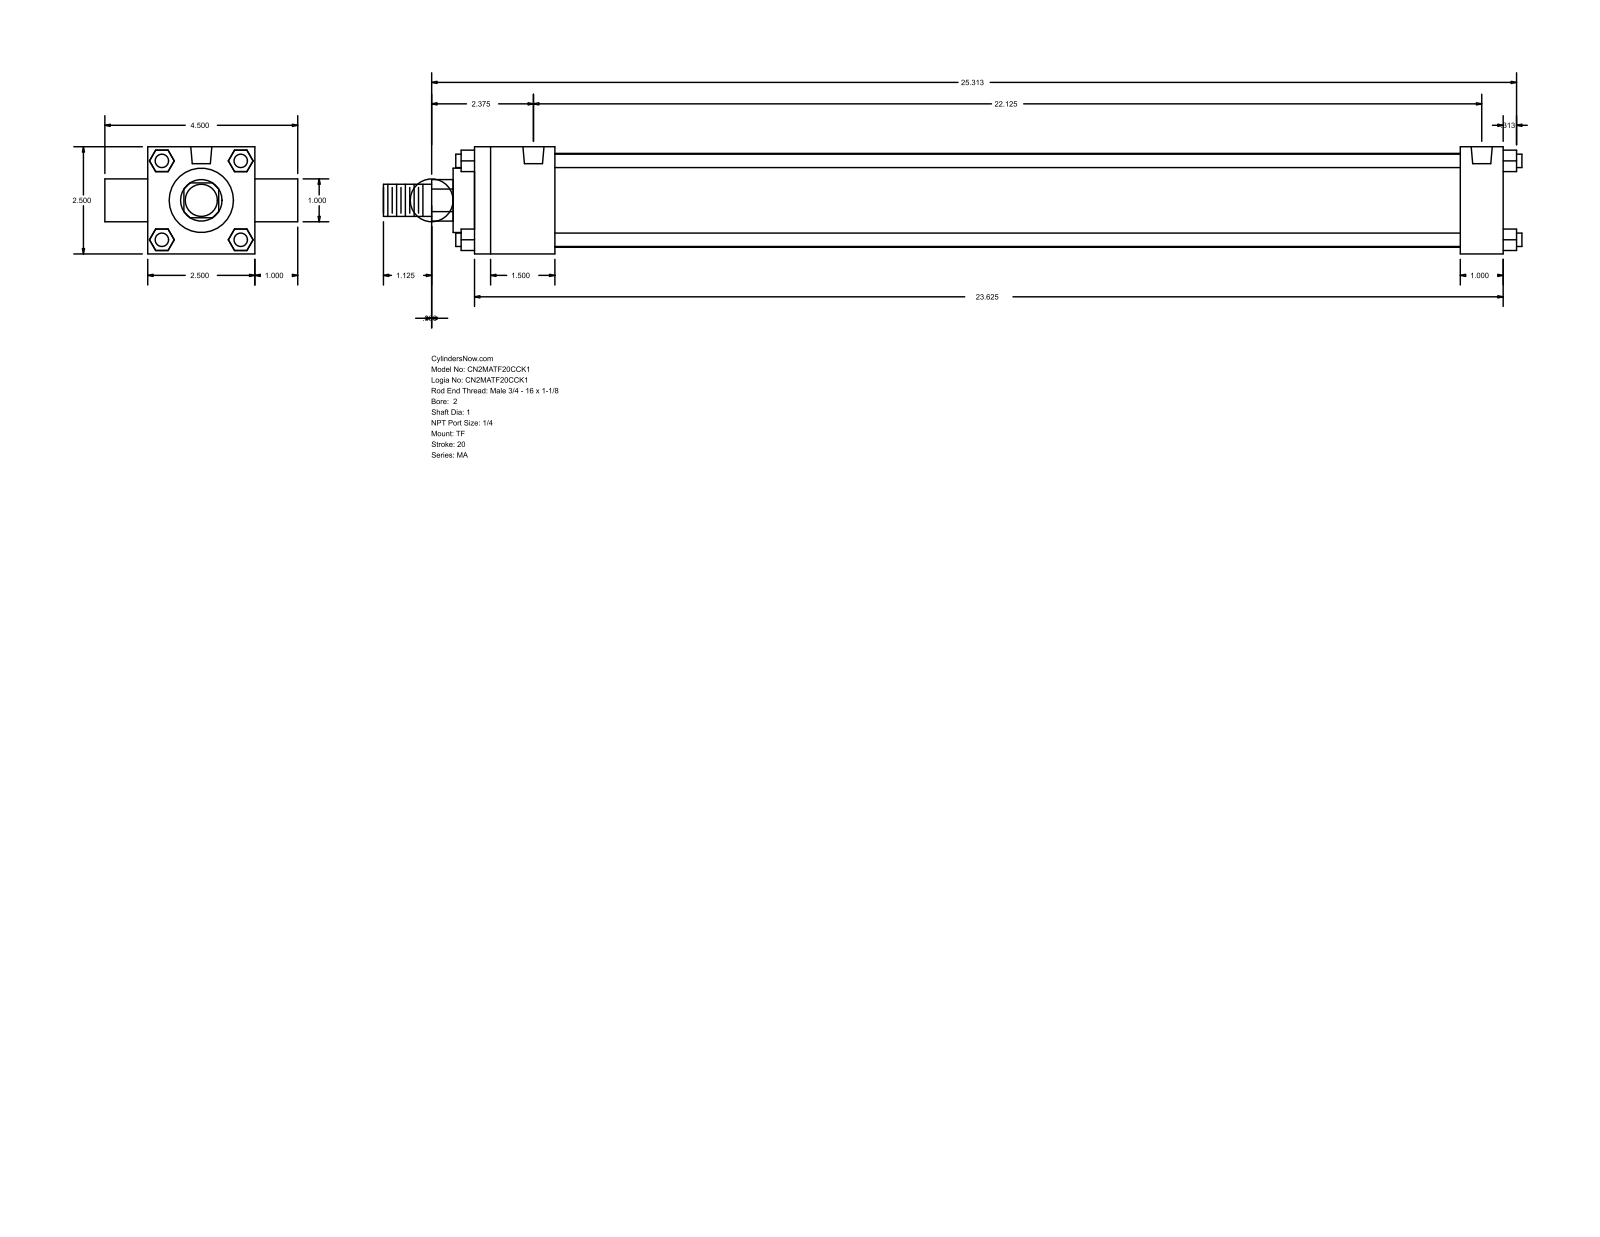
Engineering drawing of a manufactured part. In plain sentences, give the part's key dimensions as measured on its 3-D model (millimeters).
The part is named "MA_TF__0200_1". Its 3-D file was written by "GSSL Pune (CONFIG_CONTROL_DESIGN)". It is 0 solids with 120 faces: 92 planar, 28 cylindrical and 0 other. Overall it measures 674.69 by 114.3 by 63.5 millimeters. Round holes: 3 of diameter 7.94, 2 of diameter 12.49. Round bosses or shafts: 4 of diameter 7.94, 2 of diameter 25.4, 1 of diameter 55.63, 1 of diameter 38.1, 1 of diameter 19.05. Partial cylindrical surfaces (rounded edges, fillets, slot ends): 1 of radius 12.29. The main face-to-face distances are 63.5, 25.4, 609.6, 12.7, 47.63, 584.2, 536.57, 561.97, 88.9, 40.47. The hole center spacings are 561.97.
